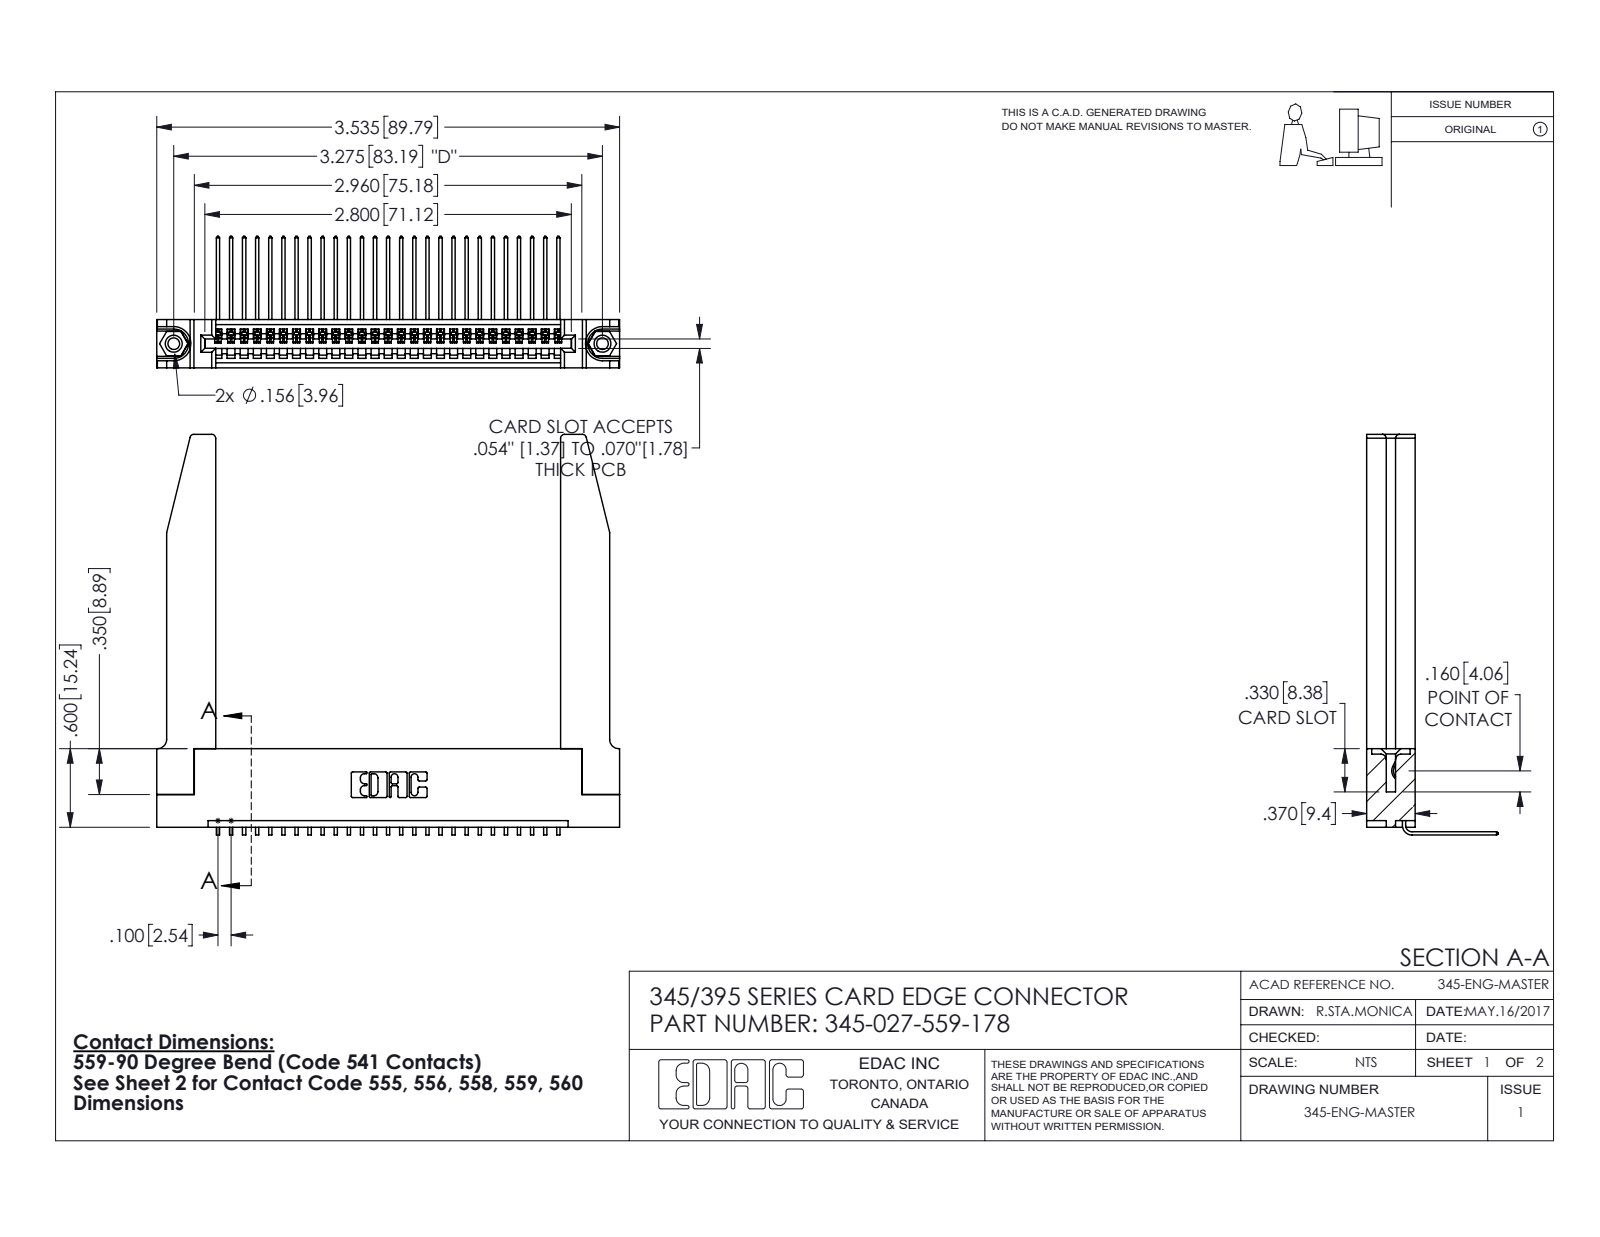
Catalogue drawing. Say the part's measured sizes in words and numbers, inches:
The part is named "345-220-078_345-220-078; 345-292-001_558 559 Tail - 1; 345 Part_Flush Mounting Lugs - 0.156 Dia-TH; 345-250-001_345-250-001-102 (+1 more)". Its 3-D file was written by "SolidWorks 2016 (CONFIG_CONTROL_DESIGN)". It is 32 solids with 1980 faces: 1356 planar, 572 cylindrical and 52 other. Overall it measures 3.536 by 3.059 by 1.005 inches. Its volume is 0.993 cubic inches and its surface area 28.62 square inches. Round holes: 2 of diameter 0.089, 2 of diameter 0.125, 2 of diameter 0.156, 1 of diameter 0.064. Round bosses or shafts: 2 of diameter 0.155. Partial cylindrical surfaces (rounded edges, fillets, slot ends): 54 of radius 0.006, 22 of radius 0.01, 8 of radius 0.03, 6 of radius 0.007, 6 of radius 0.031, 3 of radius 0.026, 2 of radius 0.031, 2 of radius 0.04. The main face-to-face distances are 0.37, 0.072, 0.298, 0.2, 0.098, 0.272, 0.025, 0.148, 0.15, 0.225. The hole center spacings are 0.27, 3.04, 3.275.
